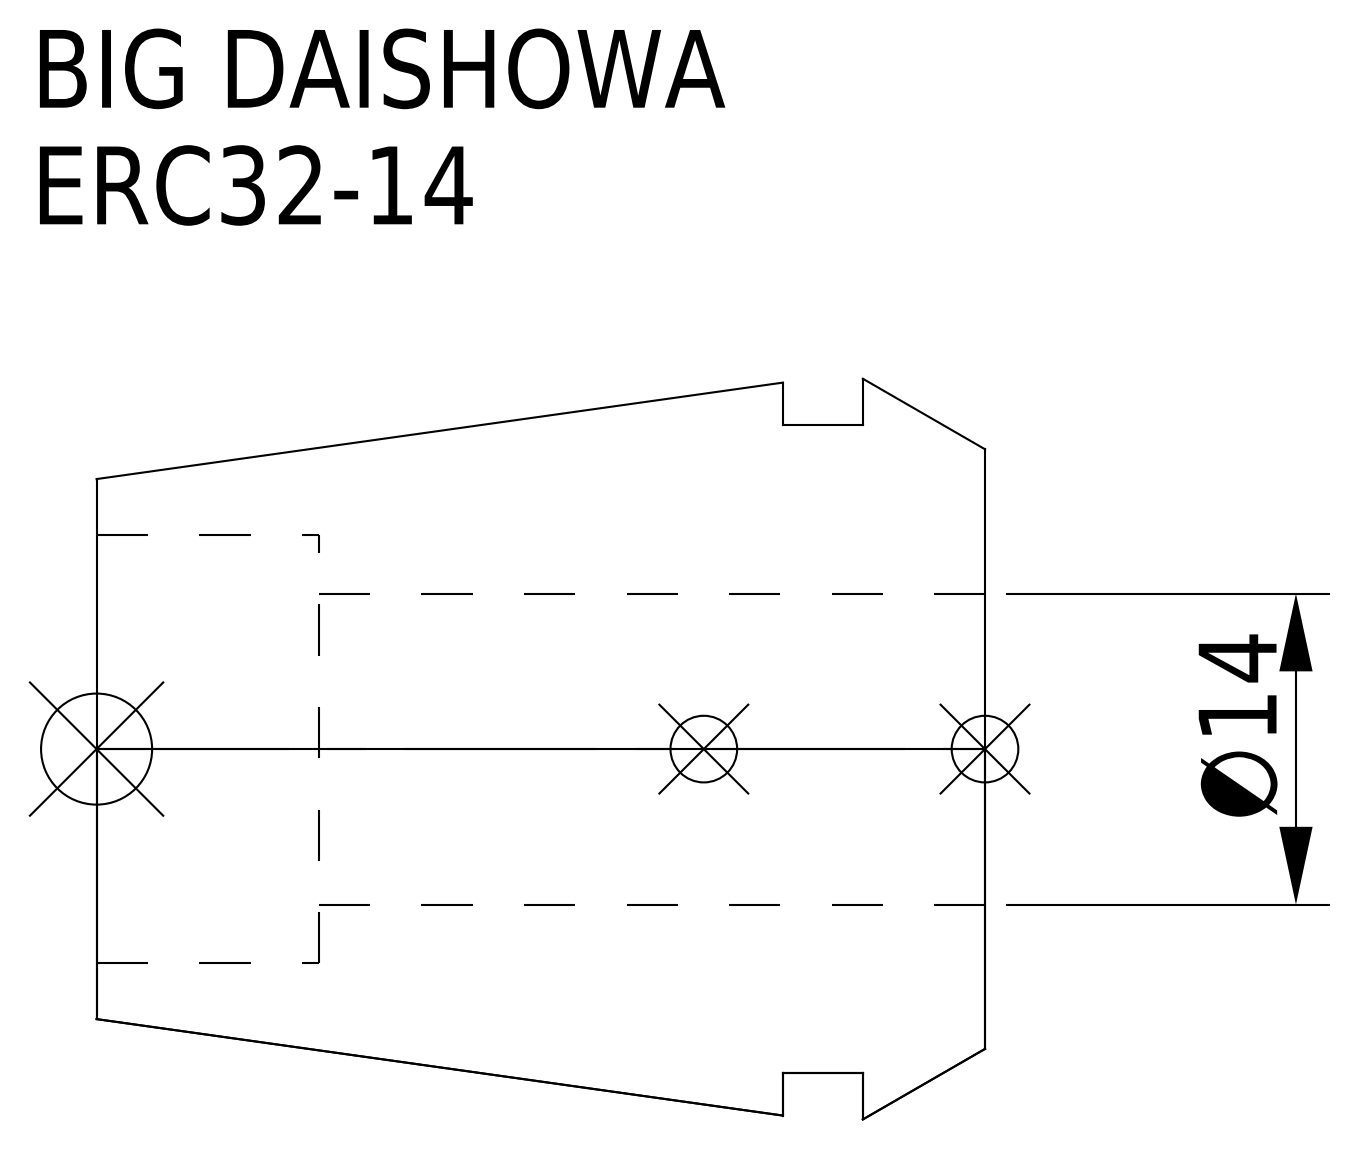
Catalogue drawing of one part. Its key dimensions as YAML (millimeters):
part_name: "ERC32-14"
step_written_by: "CREO PARAMETRIC BY PTC INC, 2016380 (AUTOMOTIVE_DESIGN)"
units: millimeters
bodies: {solids: 1, faces: 15, planar: 5, cylindrical: 6, other: 4}
overall_size: [40, 33.35, 33.35]
volume: 18899
surface_area: 6786
round_holes:
  - {diameter: 14, count: 1}
  - {diameter: 19.3, count: 1}
round_bosses_or_shafts:
  - {diameter: 29.2, count: 1}
face_to_face_distances: [5.5, 9.1, 3.6, 40, 34.5, 30.9, 30, 24.5, 20.9, 10]
